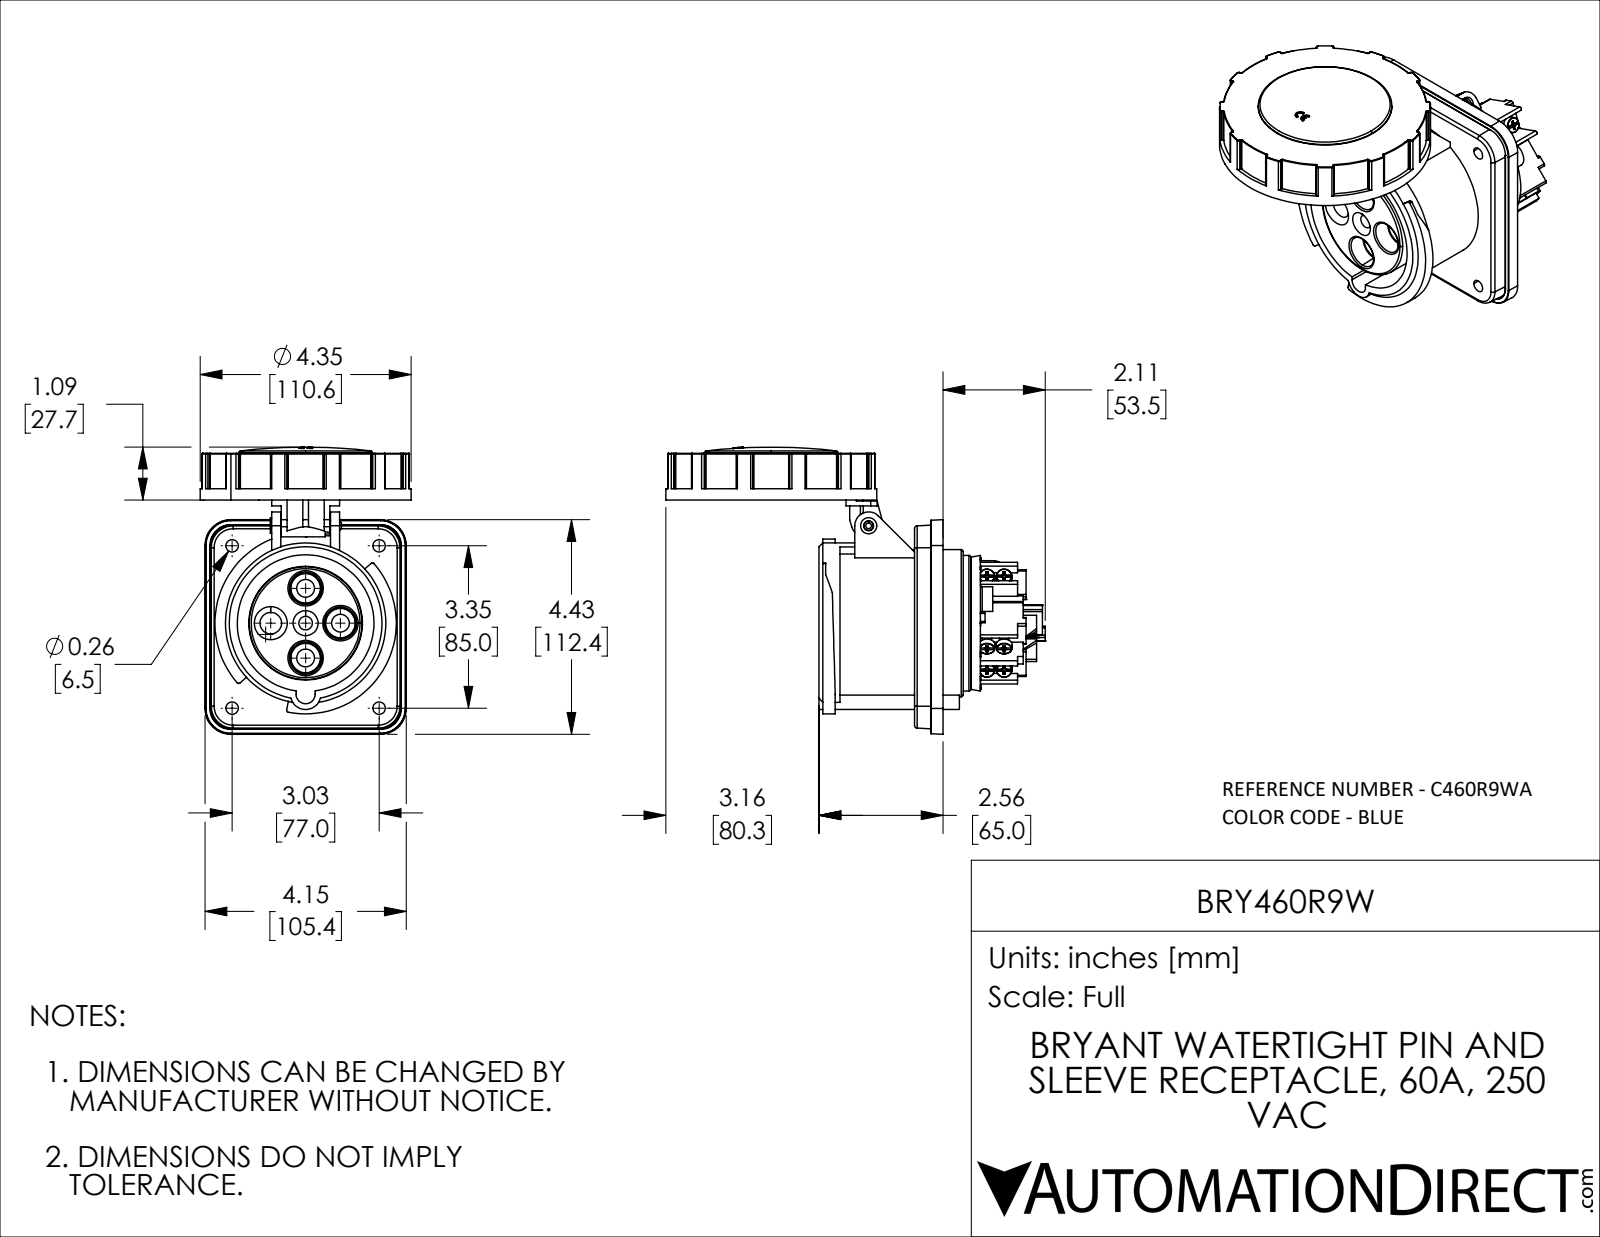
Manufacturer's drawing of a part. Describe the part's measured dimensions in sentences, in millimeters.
The part is named "BRY460R9W". Its 3-D file was written by "SolidWorks 2021 (CONFIG_CONTROL_DESIGN)". It is 2 solids with 1749 faces: 748 planar, 557 cylindrical and 444 other. Overall it measures 198.78 by 150.35 by 110.55 millimeters. Its volume is 649 280 cubic millimeters and its surface area 137 182 square millimeters. Round holes: 4 of diameter 6.5, 3 of diameter 9, 3 of diameter 9.3, 1 of diameter 3, 1 of diameter 5, 1 of diameter 5.1, 1 of diameter 7.1, 1 of diameter 8.5, 1 of diameter 11.3, 1 of diameter 71.6, 1 of diameter 81, 1 of diameter 100.6. Round bosses or shafts: 9 of diameter 5, 1 of diameter 110.55, 1 of diameter 84, 1 of diameter 77, 1 of diameter 71, 1 of diameter 70, 1 of diameter 69.33, 1 of diameter 13. Partial cylindrical surfaces (rounded edges, fillets, slot ends): 85 of radius 0.5, 48 of radius 0.3, 45 of radius 1, 8 of radius 0.25, 8 of radius 2.5, 7 of radius 0.15, 6 of radius 1.01, 6 of radius 1.28. The main face-to-face distances are 15, 19.5, 63, 48, 24.5, 2, 58.5, 11, 6.5, 82.5. The hole center spacings are 18.25, 25.81, 27.75, 36.5, 44.47, 45.28, 46.6, 48.89.
